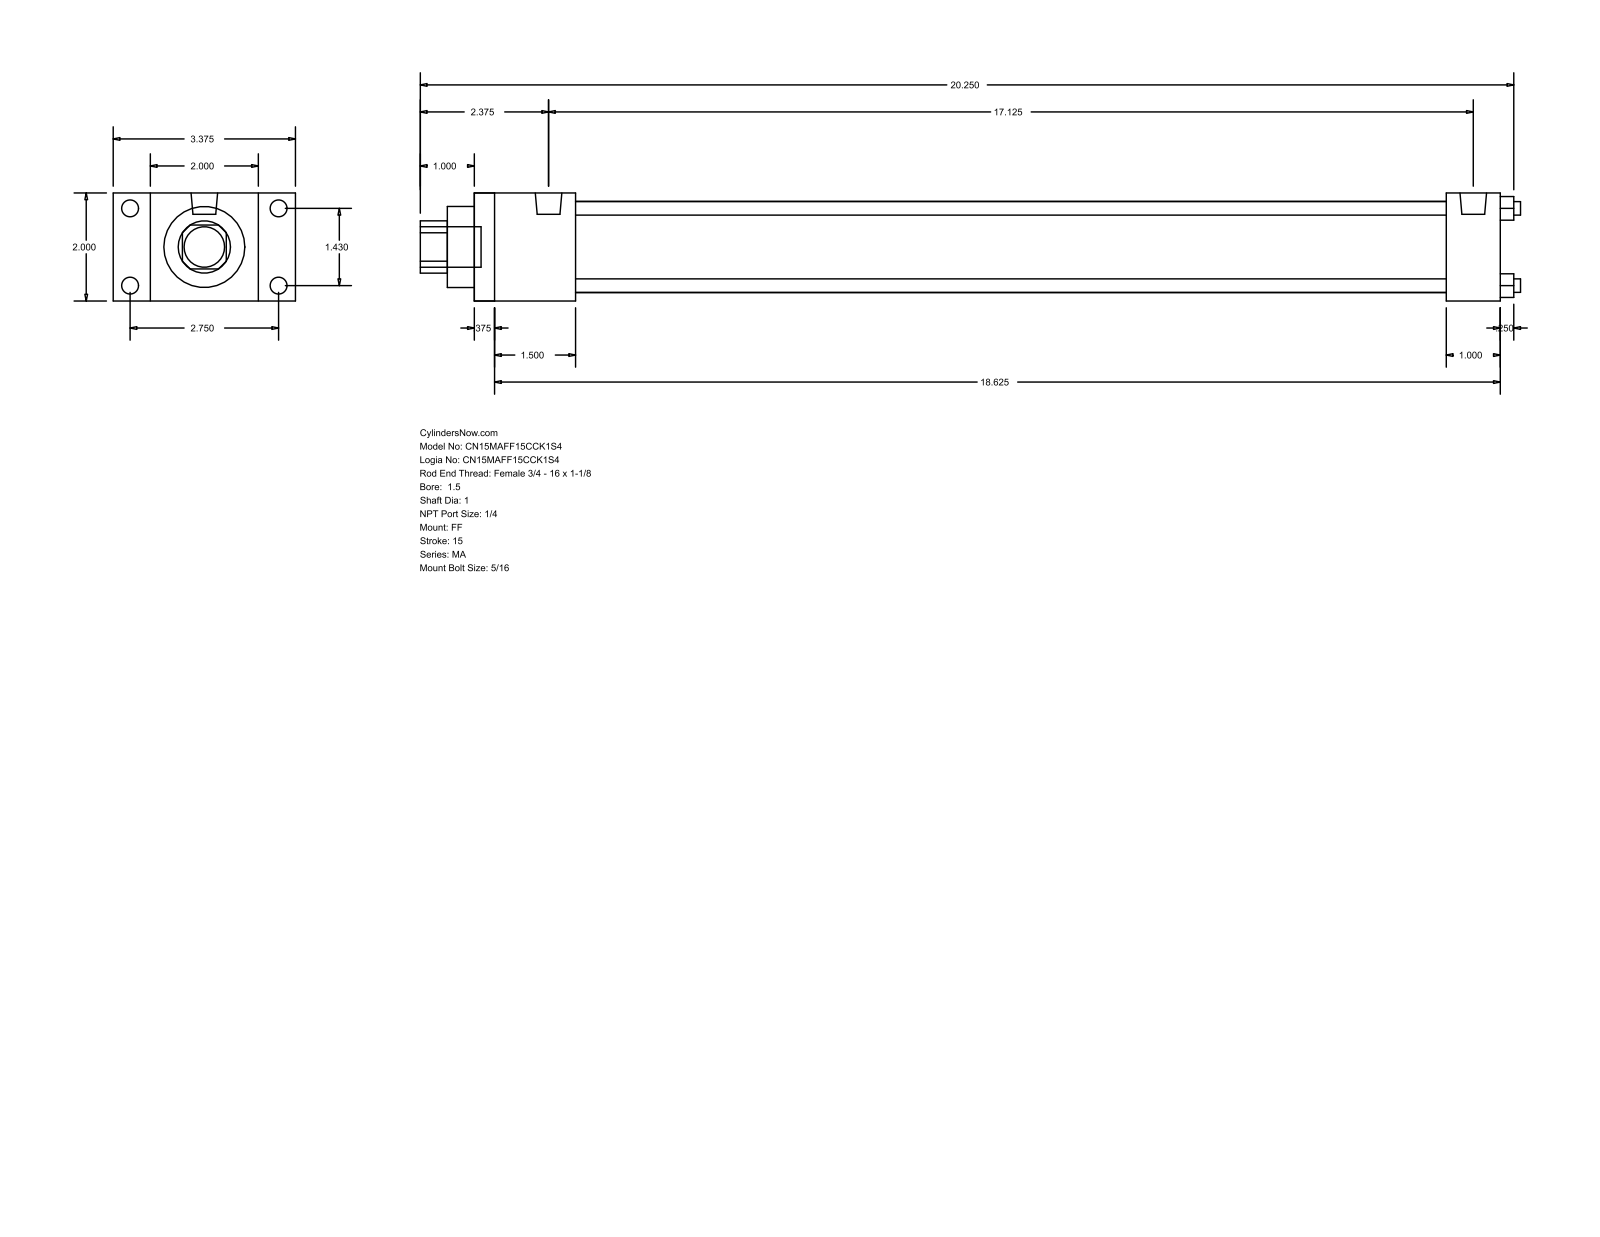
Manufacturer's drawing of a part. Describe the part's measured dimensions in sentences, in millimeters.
The part is named "MA_FF__0150_1". Its 3-D file was written by "GSSL Pune (CONFIG_CONTROL_DESIGN)". It is 0 solids with 92 faces: 64 planar, 28 cylindrical and 0 other. Overall it measures 517.52 by 85.72 by 50.8 millimeters. Round holes: 4 of diameter 6.35, 1 of diameter 25.4, 1 of diameter 38.1, 1 of diameter 42.93. Round bosses or shafts: 8 of diameter 7.94, 2 of diameter 12.49, 1 of diameter 19.05. Partial cylindrical surfaces (rounded edges, fillets, slot ends): 1 of radius 12.29. The main face-to-face distances are 50.8, 482.6, 9.52, 473.08, 25.4, 47.63, 457.2, 38.11, 447.68, 409.57. The hole center spacings are 25.68, 36.32, 51.36.
